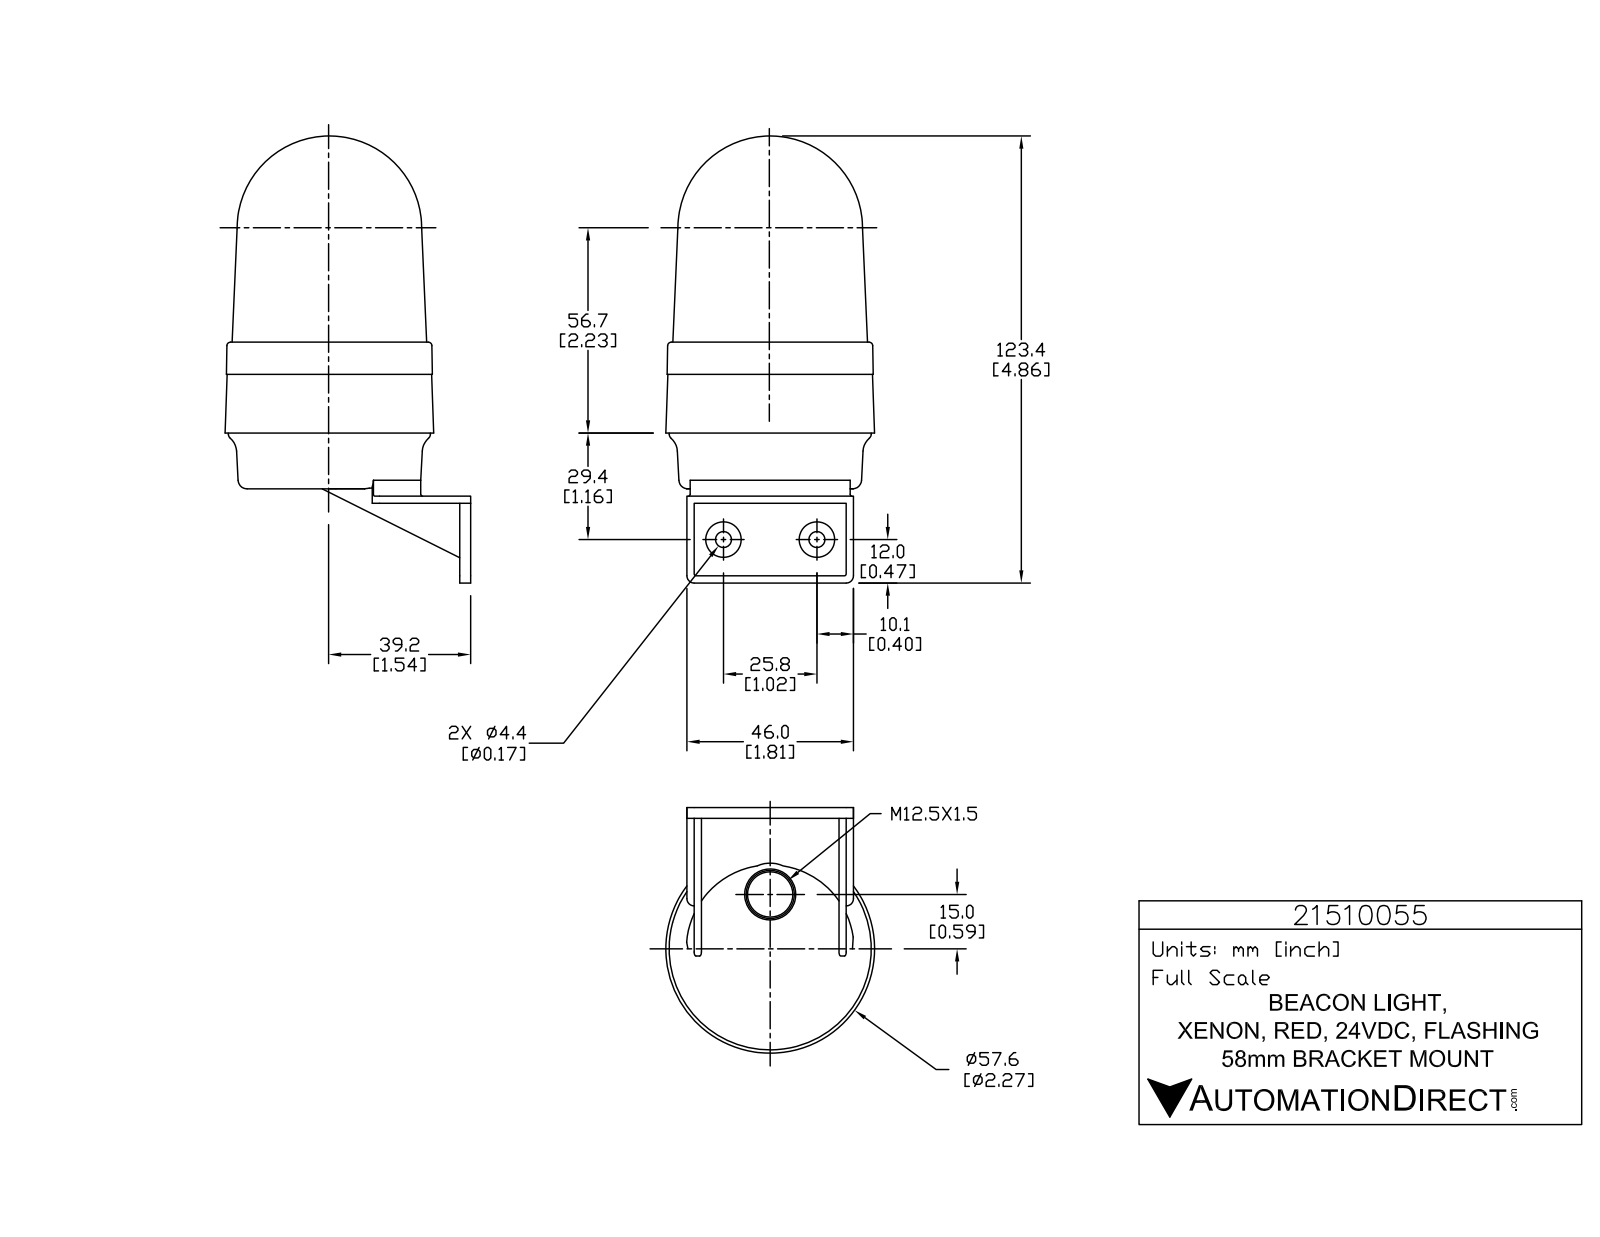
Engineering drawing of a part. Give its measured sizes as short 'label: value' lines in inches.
name: 21510055
written by: SolidWorks 2015 (AUTOMOTIVE_DESIGN)
unit: in
bodies: 1 solid, 828 faces (551 planar, 179 cylindrical, 98 other)
size: 4.858 × 2.852 × 2.407
volume: 12.43 in³; area: 37.49 in²
holes: 3× ⌀0.039, 2× ⌀0.173
bosses: 3× ⌀0.226, 3× ⌀0.056, 2× ⌀0.386, 1× ⌀2.197
rounds: 6× R0.008, 6× R0.008, 6× R0.008, 6× R0.02, 6× R0.131, 4× R0.079, 3× R0.004, 3× R0.005
face distances: 0.079, 0.157, 1.575, 1.654, 0.039, 0.118, 1.496, 0.866, 0.945, 0.764
hole spacings: 1.016
